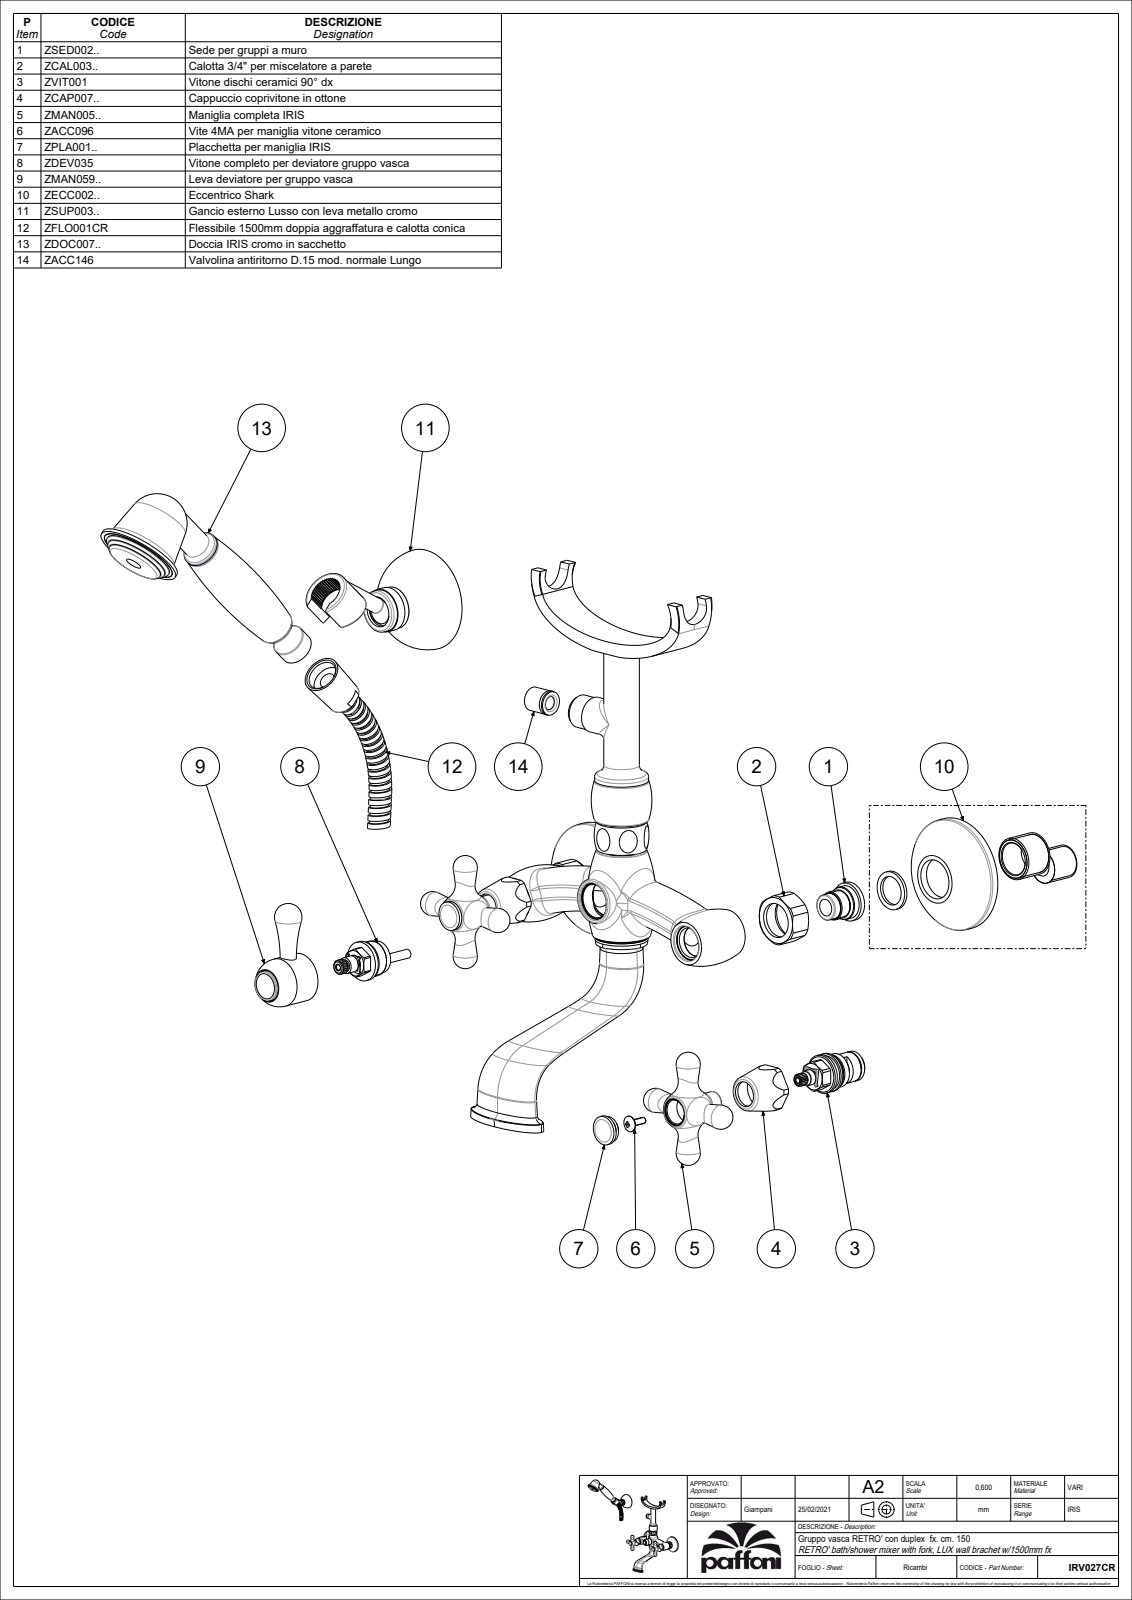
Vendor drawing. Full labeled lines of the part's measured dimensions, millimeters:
Part name (STEP PRODUCT): IRV027CR
STEP written by: CREO PARAMETRIC BY PTC INC, 2020044 (CONFIG_CONTROL_DESIGN)
Units: millimetres
Bodies: 7 solids, 919 faces (240 planar, 155 cylindrical, 524 other)
Overall size (bounding box): 404.63 × 367.5 × 243.29
Volume: 687 956 mm³ · Surface area: 187 666 mm²
Round holes (diameter × count): ⌀21.5 ×3, ⌀23 ×3, ⌀24.1 ×3, ⌀8 ×2, ⌀15.7 ×2, ⌀16.7 ×2, ⌀18.63 ×2, ⌀19 ×2, ⌀21 ×2, ⌀26.7 ×2, ⌀14.5 ×1, ⌀15 ×1
Round bosses / shafts (diameter × count): ⌀18 ×3, ⌀70 ×2, ⌀22 ×2, ⌀13.5 ×2, ⌀53 ×1, ⌀44 ×1, ⌀40 ×1, ⌀36 ×1
Partial cylindrical surfaces — rounded edges, fillets, slot ends (radius × count): R10 ×2, R14.5 ×2, R15.5 ×2, R14 ×1
Main face-to-face distances: 44, 20, 23.25, 3.25, 26.5, 15.5, 24, 35.5, 29, 6.5
Hole centre spacings: 76.3, 150
